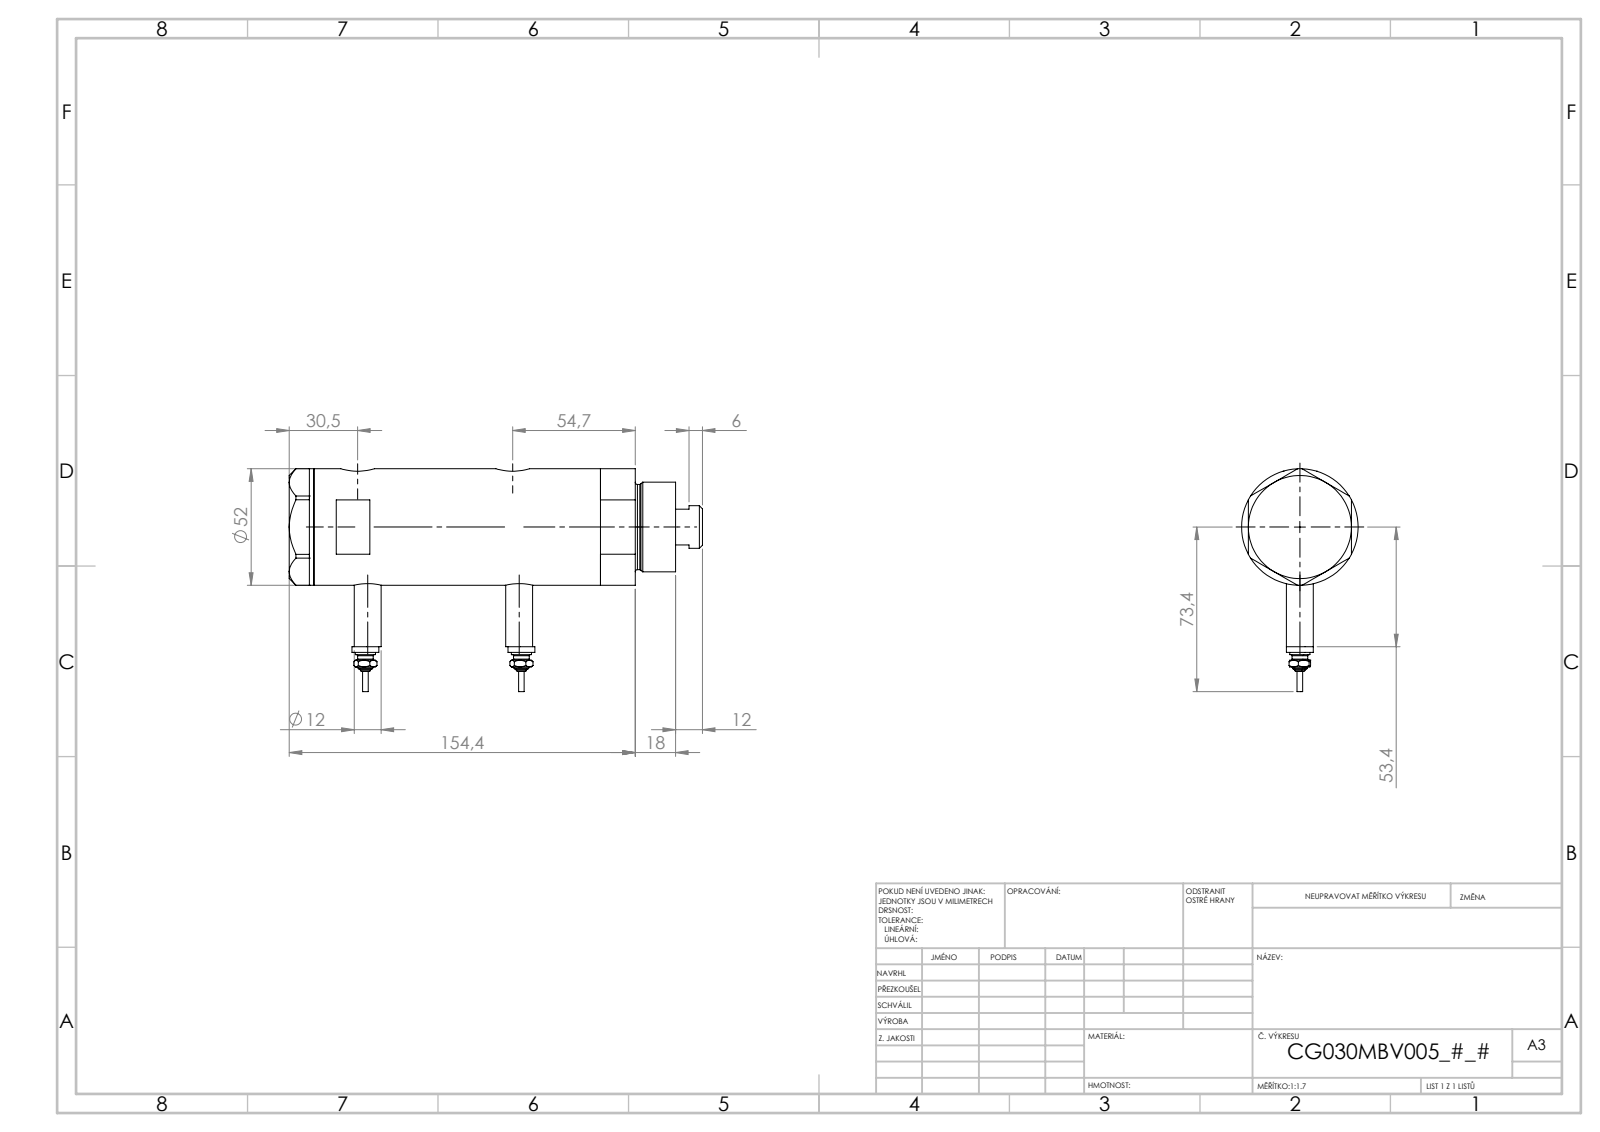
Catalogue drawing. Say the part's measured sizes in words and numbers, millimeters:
The part is named "V270CG_SWITCH; V270CG_VC; V270CG_MIDDLE; V270CG_FRONT (+1 more)". Its 3-D file was written by "SolidWorks 2019 (CONFIG_CONTROL_DESIGN)". It is 6 solids with 246 faces: 95 planar, 77 cylindrical and 74 other. Overall it measures 154.02 by 84.3 by 52 millimeters. Its volume is 279 030 cubic millimeters and its surface area 68 638 square millimeters. Round holes: 2 of diameter 5, 2 of diameter 9.73, 2 of diameter 12.5, 2 of diameter 15, 1 of diameter 6.5, 1 of diameter 20, 1 of diameter 21.5, 1 of diameter 30, 1 of diameter 33, 1 of diameter 44. Round bosses or shafts: 3 of diameter 12, 2 of diameter 9, 2 of diameter 7, 2 of diameter 4.34, 2 of diameter 2.4, 1 of diameter 52, 1 of diameter 40, 1 of diameter 38. The main face-to-face distances are 58.56, 23.8, 34.76, 11, 34.8, 69.56, 46, 105.96, 94.96, 71.16. The hole center spacings are 2.9, 4.5, 31.75, 34.65, 36.25, 39.15, 2.89, 2.91.
